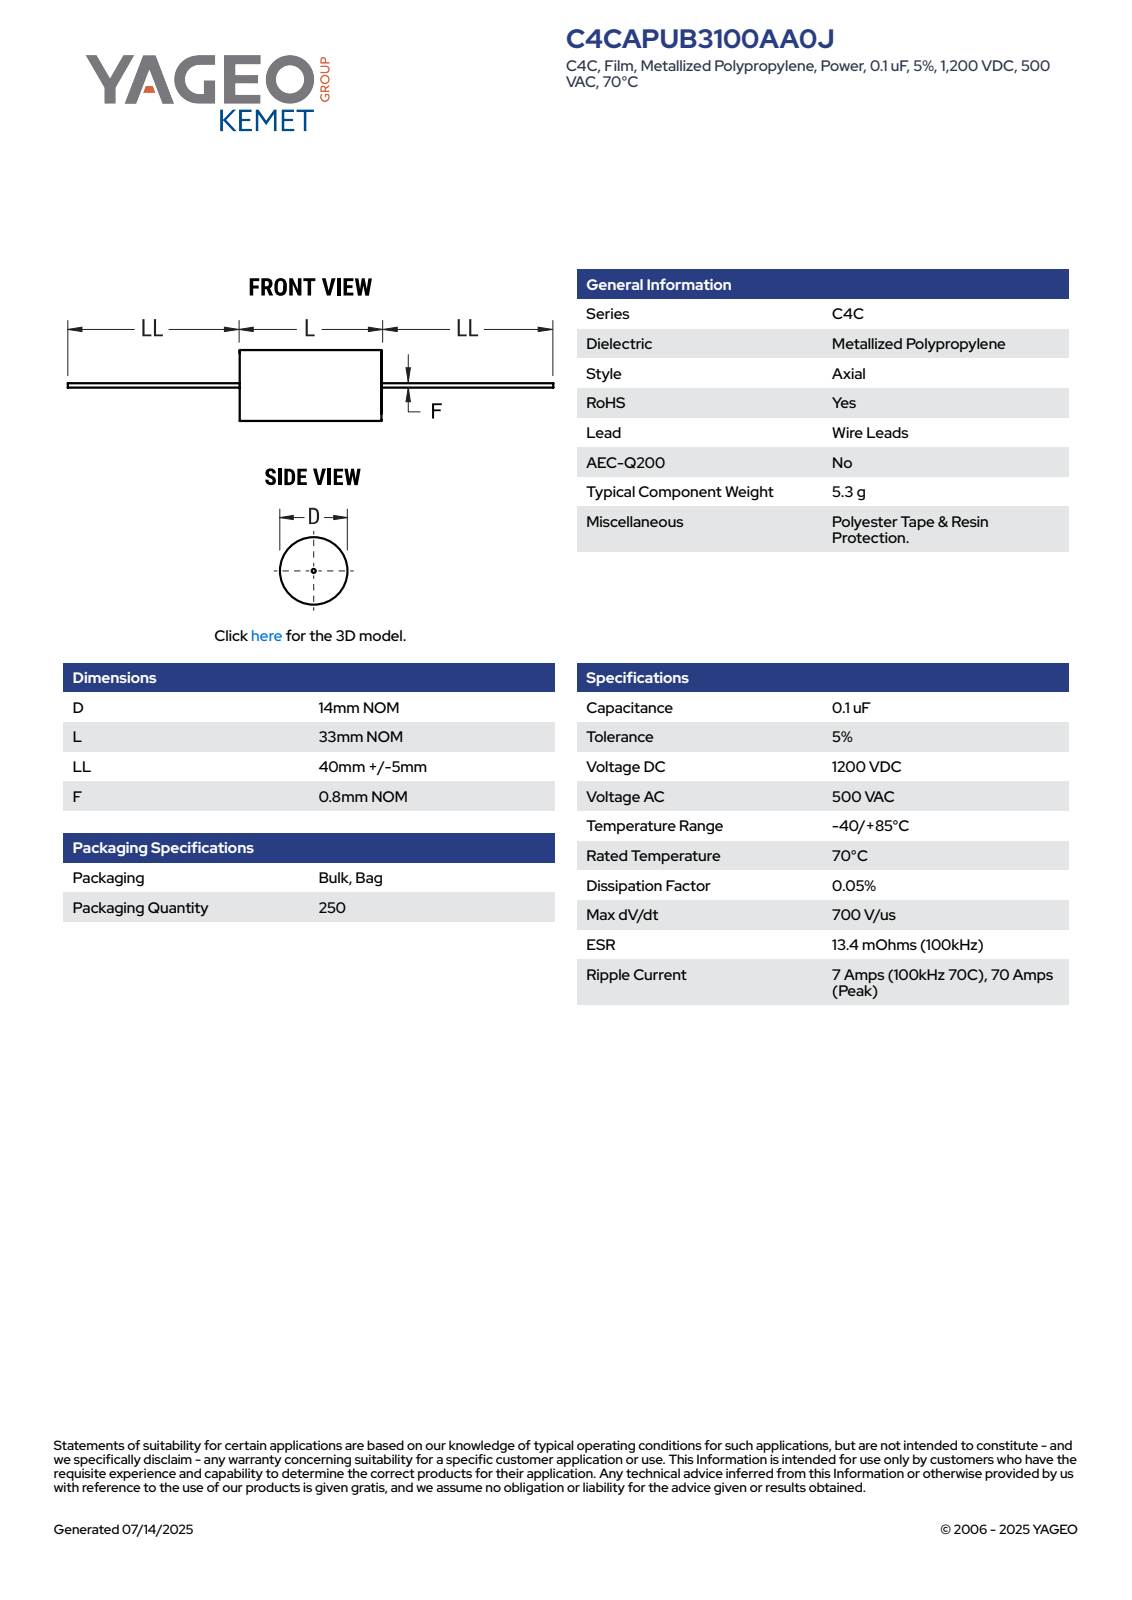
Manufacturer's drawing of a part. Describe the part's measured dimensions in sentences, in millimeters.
The part is named "CFP_ACWF_14X33_D14L33LL45F0.8". Its 3-D file was written by "SolidWorks 2014 (AUTOMOTIVE_DESIGN)". It is 2 solids with 87 faces: 28 planar, 28 cylindrical and 31 other. Overall it measures 123 by 14 by 14 millimeters. Its volume is 5 125 cubic millimeters and its surface area 2 293 square millimeters. Round bosses or shafts: 1 of diameter 14, 1 of diameter 0.8. Partial cylindrical surfaces (rounded edges, fillets, slot ends): 1 of radius 6.99. The main face-to-face distances are 33, 33.01, 45, 78, 44.99, 123, 78.01.
